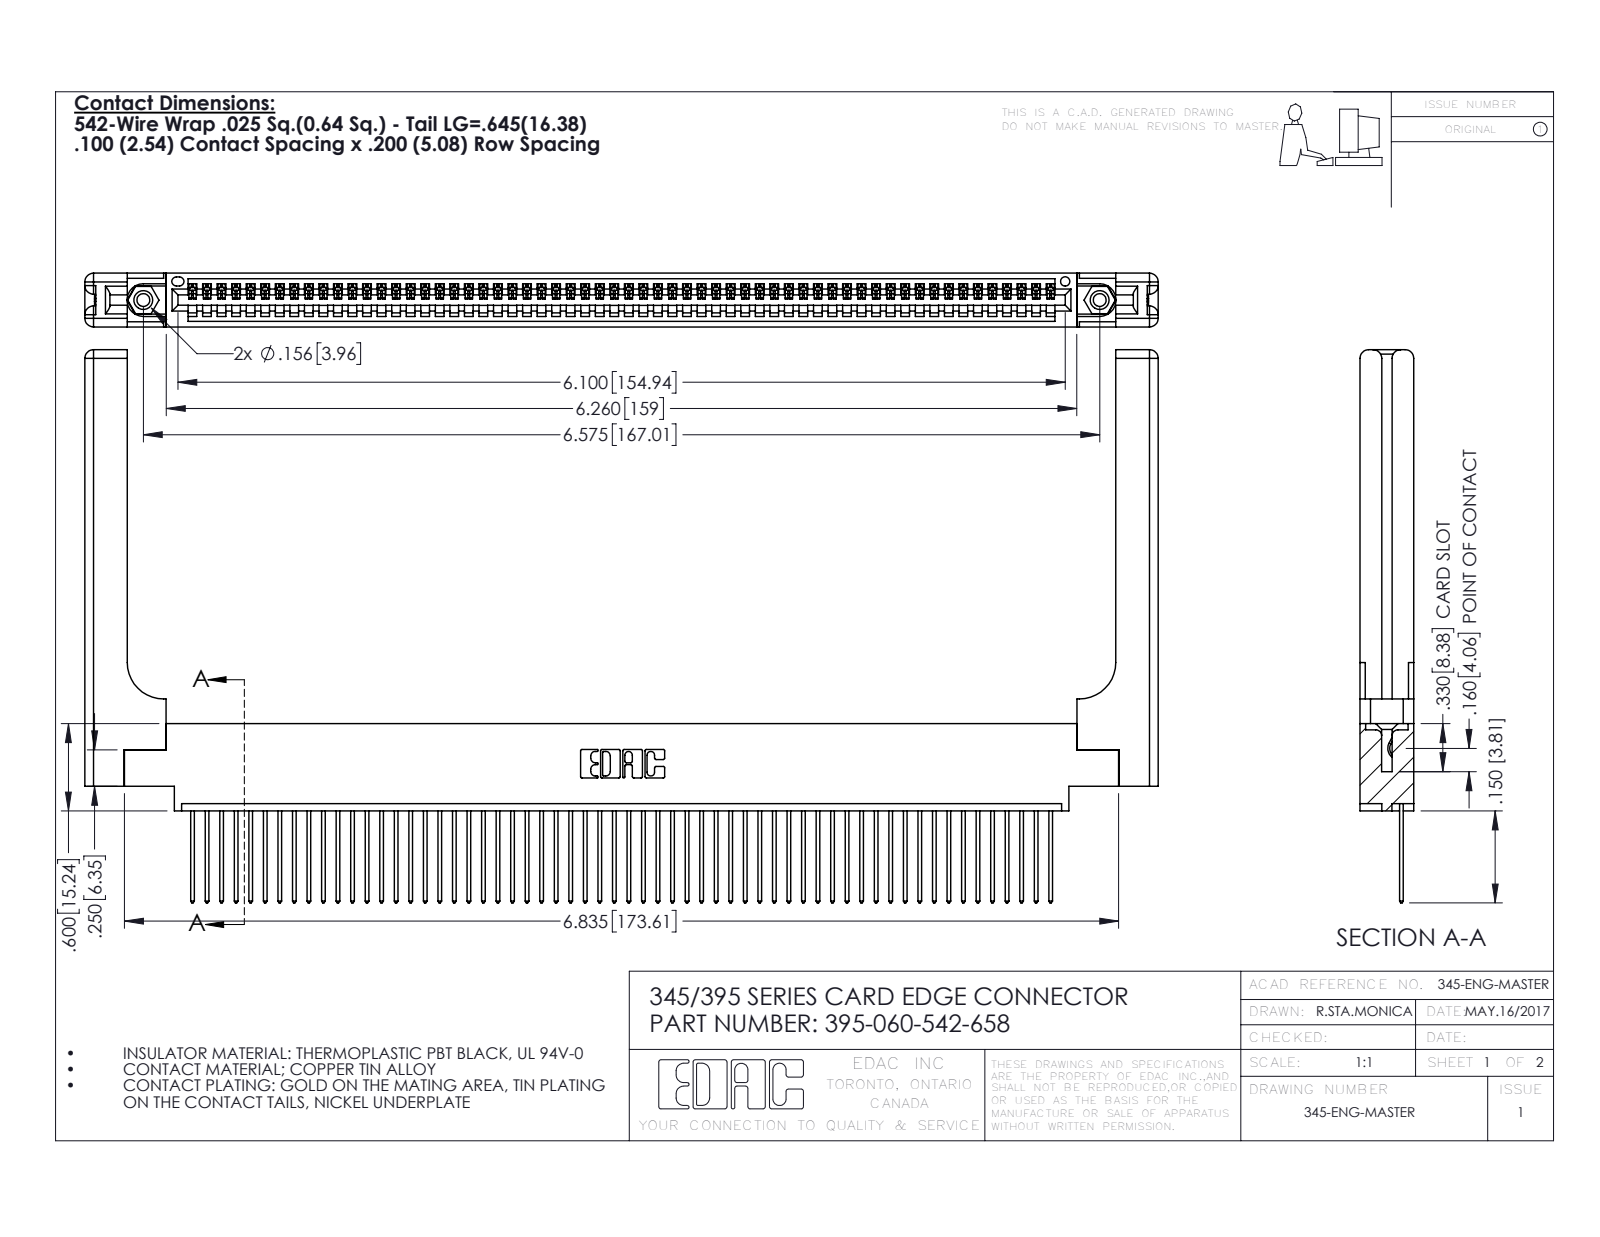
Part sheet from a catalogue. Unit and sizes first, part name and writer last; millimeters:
Units: millimetres
Overall size (bounding box): 187.4 × 96.6 × 9.4
Round holes (diameter × count): ⌀2.3 ×2, ⌀3.2 ×2, ⌀4 ×2, ⌀1.6 ×1
Round bosses / shafts (diameter × count): ⌀3.9 ×2
Partial cylindrical surfaces — rounded edges, fillets, slot ends (radius × count): R0.2 ×120, R0.3 ×120, R0.3 ×22, R1.5 ×16, R0.2 ×6, R0.8 ×6, R0.7 ×3, R0.8 ×2
Main face-to-face distances: 1.8, 7.6, 9.4, 2.5, 6.9, 0.6, 5.1, 5.7, 3.8, 3.8
Hole centre spacings: 6.9, 161, 167
Volume: 26 480 mm³ · Surface area: 30 400 mm²
Bodies: 65 solids, 3866 faces (2632 planar, 1174 cylindrical, 60 other)
Part name (STEP PRODUCT): 345-220-058_345-220-058; 345 Part_0.170 Offset - 0.156 Dia-TH; 395-060-542-658; 345-292-001_345-293-142 (+1 more)
STEP written by: SolidWorks 2016 (CONFIG_CONTROL_DESIGN)
